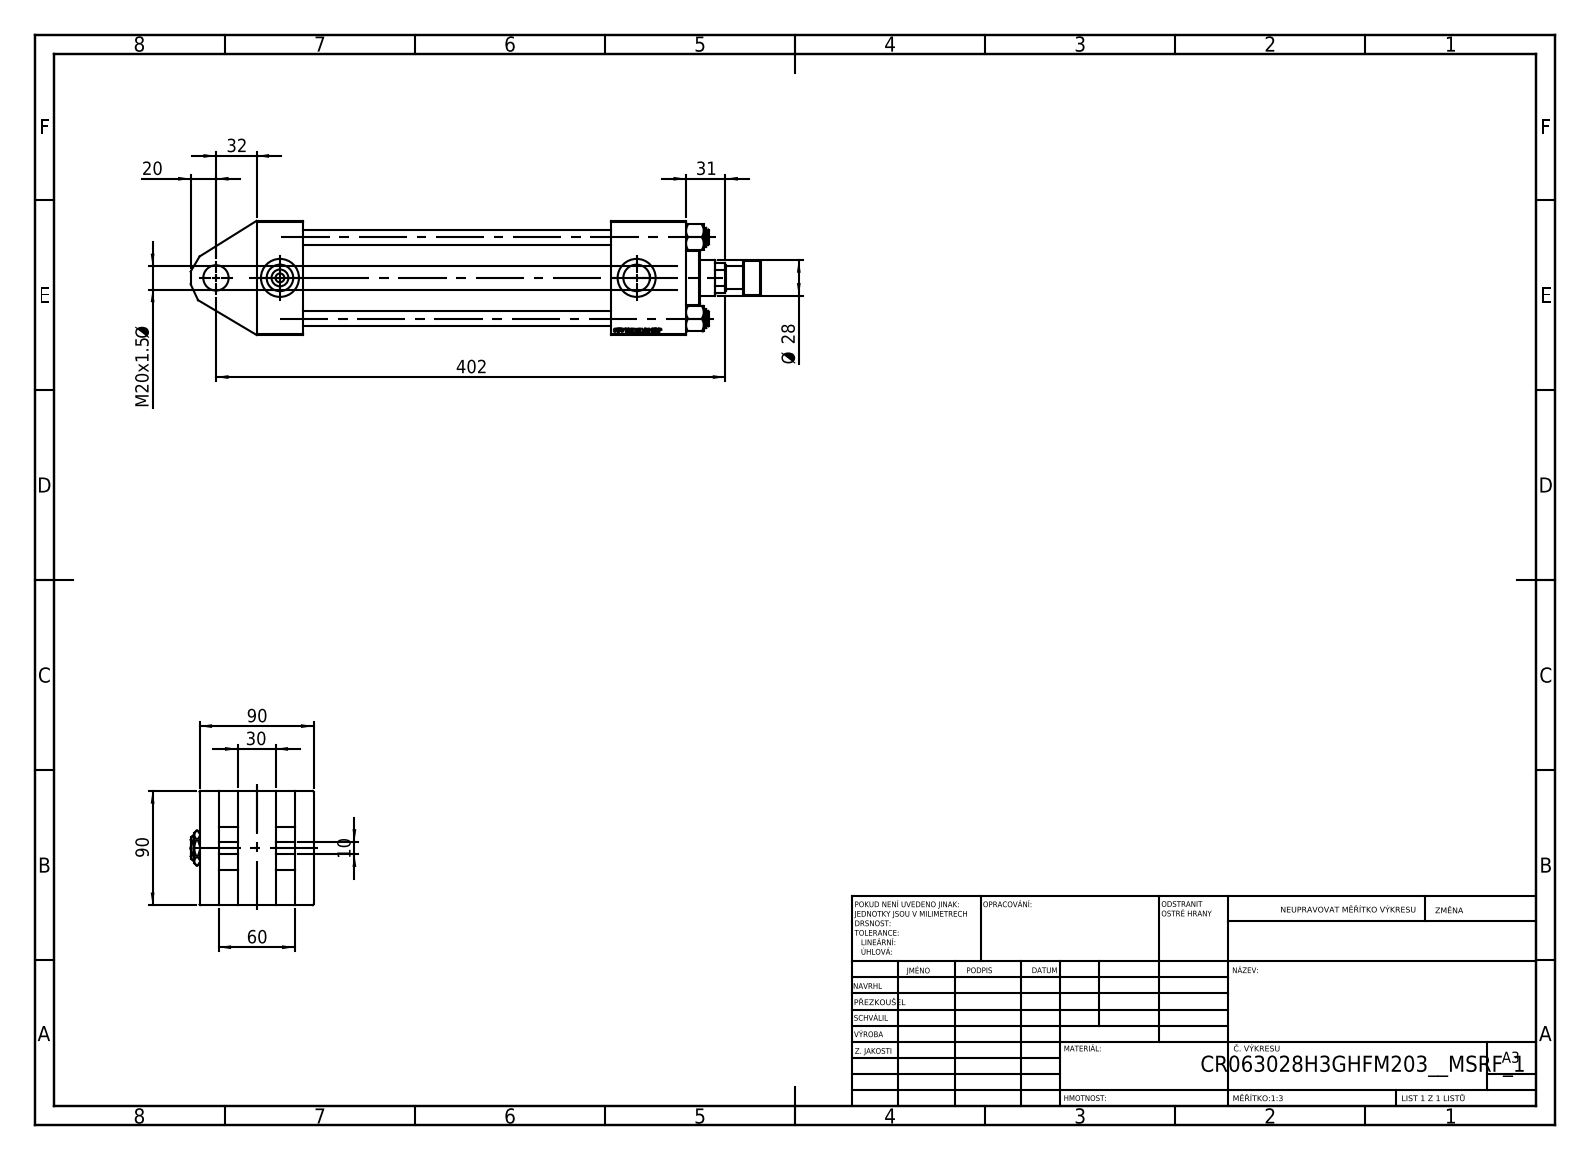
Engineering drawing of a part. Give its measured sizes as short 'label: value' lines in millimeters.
name: V215CR_H_Body; V215CR_TYCINKA_H; V215_VC_A; V215CR_VCP_H (+3 more)
written by: SolidWorks 2019 (CONFIG_CONTROL_DESIGN)
unit: mm
bodies: 14 solids, 1244 faces (570 planar, 98 cylindrical, 576 other)
size: 450 × 97 × 90
volume: 1 354 000 mm³; area: 324 800 mm²
holes: 4× ⌀12, 2× ⌀7, 2× ⌀20.96, 2× ⌀30, 1× ⌀18.5, 1× ⌀20, 1× ⌀28, 1× ⌀31, 1× ⌀50, 1× ⌀60, 1× ⌀63
bosses: 4× ⌀15, 1× ⌀69, 1× ⌀42, 1× ⌀27, 1× ⌀18
face distances: 90, 15, 60, 30, 302, 45, 37, 59, 75, 339
hole spacings: 45.47, 64.3, 90.93, 50.5, 281.5, 332
